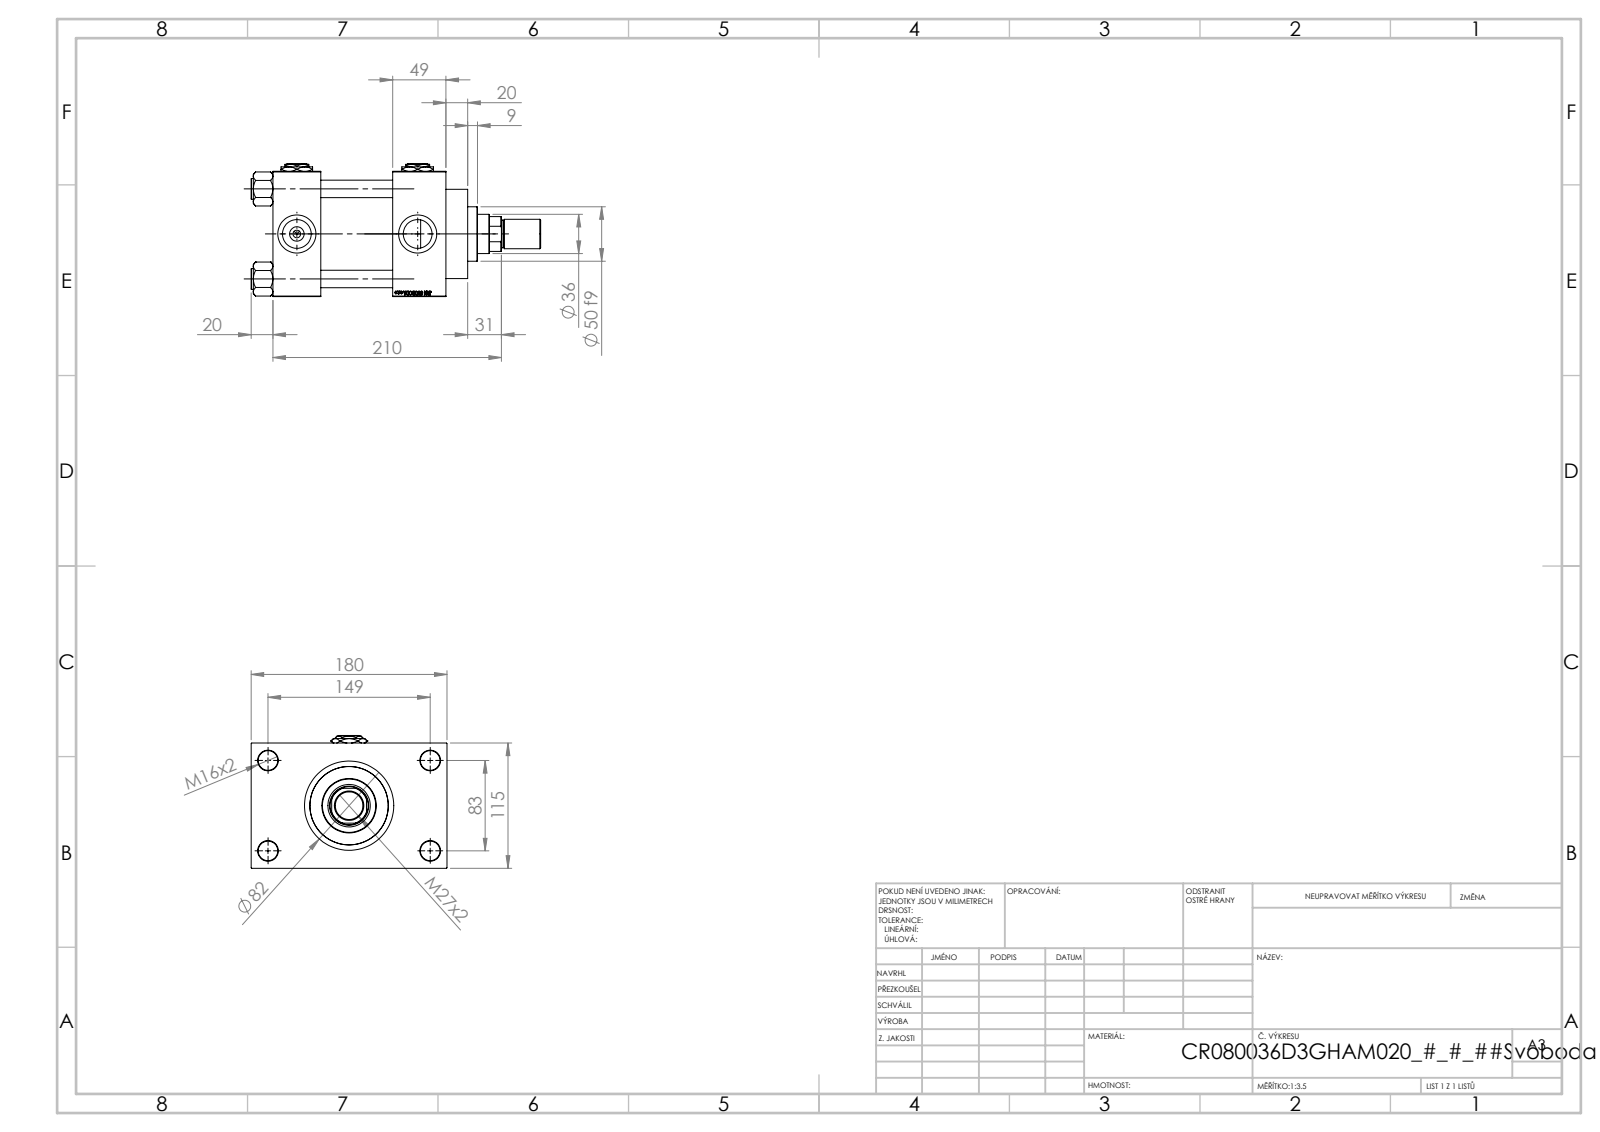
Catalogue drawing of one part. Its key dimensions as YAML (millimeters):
part_name: "Zatka_pro_OIL_PORT; V215CR_VCP_D; V215CR_D_TYCINKA; ROD_END_AH (+3 more)"
step_written_by: "SolidWorks 2019 (CONFIG_CONTROL_DESIGN)"
units: millimeters
bodies: {solids: 14, faces: 1266, planar: 597, cylindrical: 103, other: 566}
overall_size: [266, 180, 122]
volume: 1986000
surface_area: 307572
round_holes:
  - {diameter: 16, count: 4}
  - {diameter: 18, count: 4}
  - {diameter: 26.44, count: 4}
  - {diameter: 35, count: 4}
  - {diameter: 7, count: 3}
  - {diameter: 25.5, count: 1}
  - {diameter: 36, count: 1}
  - {diameter: 39, count: 1}
  - {diameter: 61, count: 1}
  - {diameter: 72, count: 1}
  - {diameter: 80, count: 1}
round_bosses_or_shafts:
  - {diameter: 19, count: 4}
  - {diameter: 86, count: 1}
  - {diameter: 82, count: 1}
  - {diameter: 50, count: 1}
  - {diameter: 27, count: 1}
  - {diameter: 25, count: 1}
partial_cylinders:
  - {radius: 17.5, count: 1}
face_to_face_distances: [115, 66, 110, 49, 44, 159, 32.5, 147.5, 20, 69]
hole_center_spacings: [33.15, 58.48, 82.7, 85.28, 89.24, 115.85, 142.43, 83]
